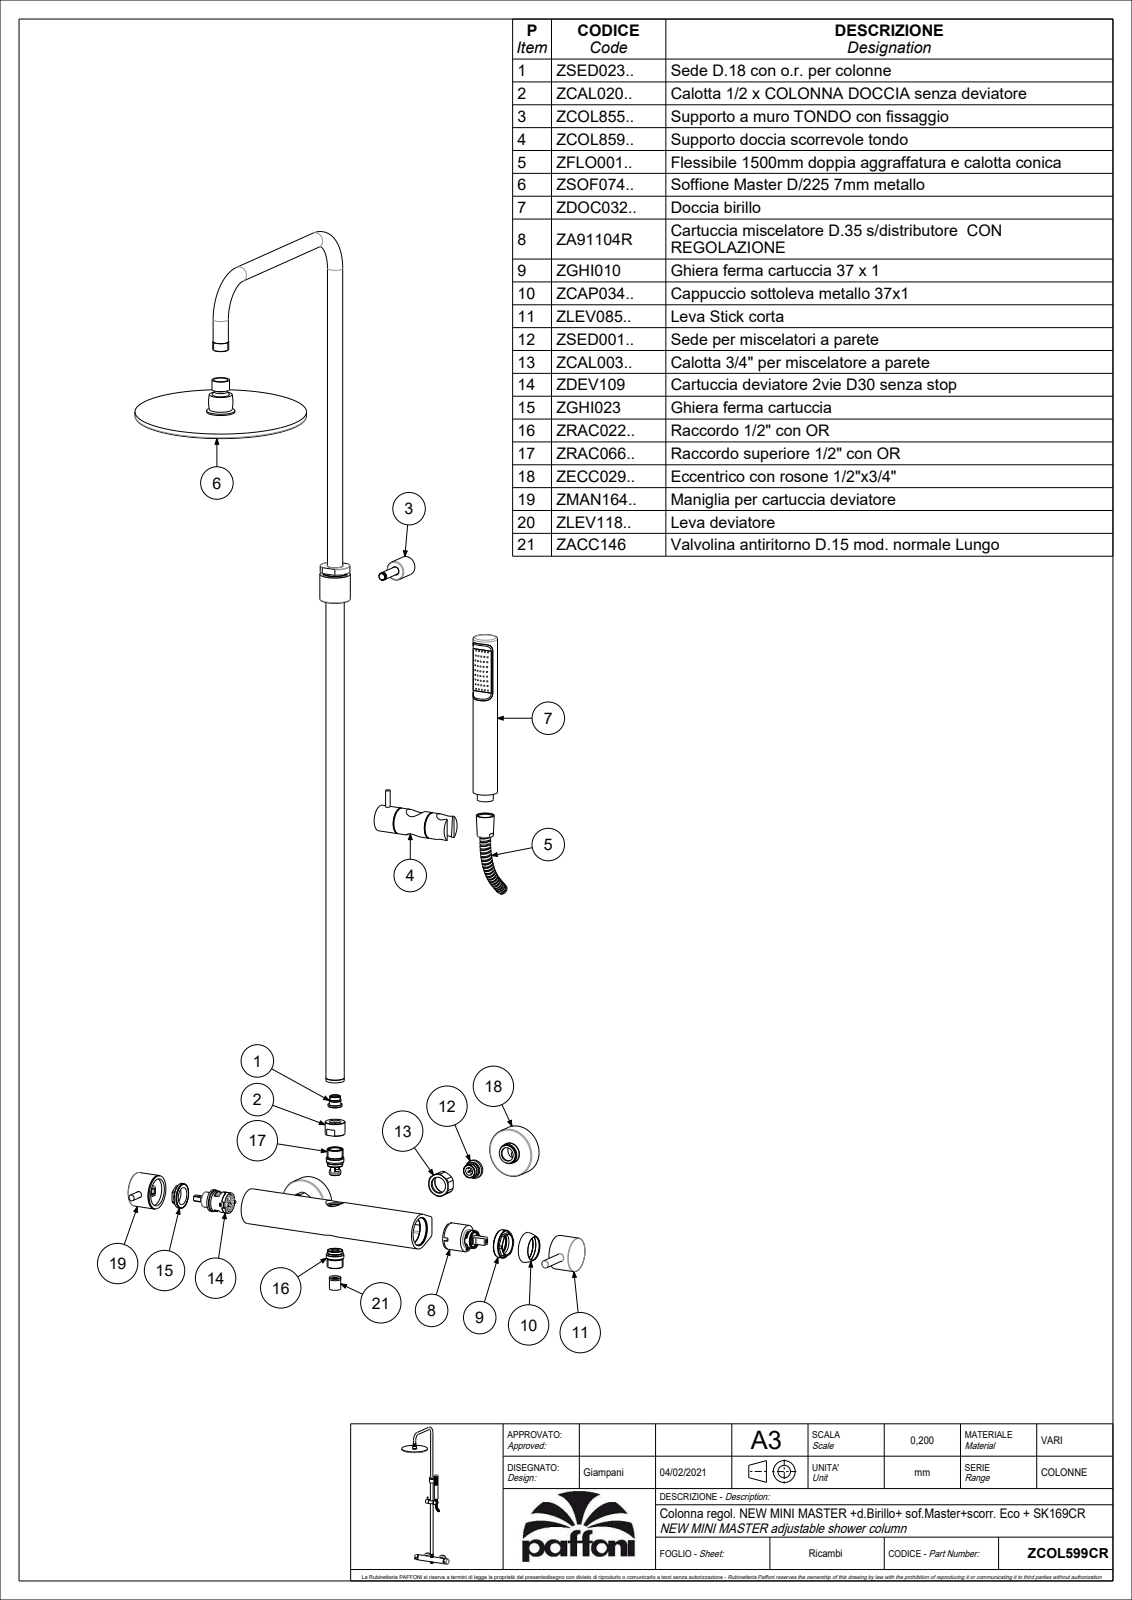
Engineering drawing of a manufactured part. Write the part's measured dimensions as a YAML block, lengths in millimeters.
part_name: "ZCOL599CR"
step_written_by: "CREO PARAMETRIC BY PTC INC, 2020044 (CONFIG_CONTROL_DESIGN)"
units: millimeters
bodies: {solids: 9, faces: 2316, planar: 621, cylindrical: 815, other: 880}
overall_size: [1241.6, 491.3, 322.59]
volume: 940217
surface_area: 571740
round_holes:
  - {diameter: 1.2, count: 80}
  - {diameter: 1.5, count: 45}
  - {diameter: 6, count: 3}
  - {diameter: 7, count: 3}
  - {diameter: 10.5, count: 3}
  - {diameter: 17, count: 3}
  - {diameter: 20, count: 3}
  - {diameter: 4.2, count: 2}
  - {diameter: 4.5, count: 2}
  - {diameter: 5, count: 2}
  - {diameter: 9.5, count: 2}
  - {diameter: 10, count: 2}
round_bosses_or_shafts:
  - {diameter: 23, count: 3}
  - {diameter: 20, count: 3}
  - {diameter: 63.5, count: 2}
  - {diameter: 44.5, count: 2}
  - {diameter: 28, count: 2}
  - {diameter: 27, count: 2}
  - {diameter: 26.2, count: 2}
  - {diameter: 21, count: 2}
partial_cylinders:
  - {radius: 2.17, count: 84}
  - {radius: 1.68, count: 30}
  - {radius: 1, count: 15}
  - {radius: 0.5, count: 12}
  - {radius: 6, count: 4}
  - {radius: 0.99, count: 2}
  - {radius: 2.17, count: 2}
  - {radius: 5.05, count: 2}
face_to_face_distances: [6.5, 3.45, 15.5, 0.6, 16.1, 14.8, 39.73, 24.93, 21.48, 3.5]
hole_center_spacings: [7.91, 13.76, 20.01, 6.5, 28.16, 90, 13, 26.39]
